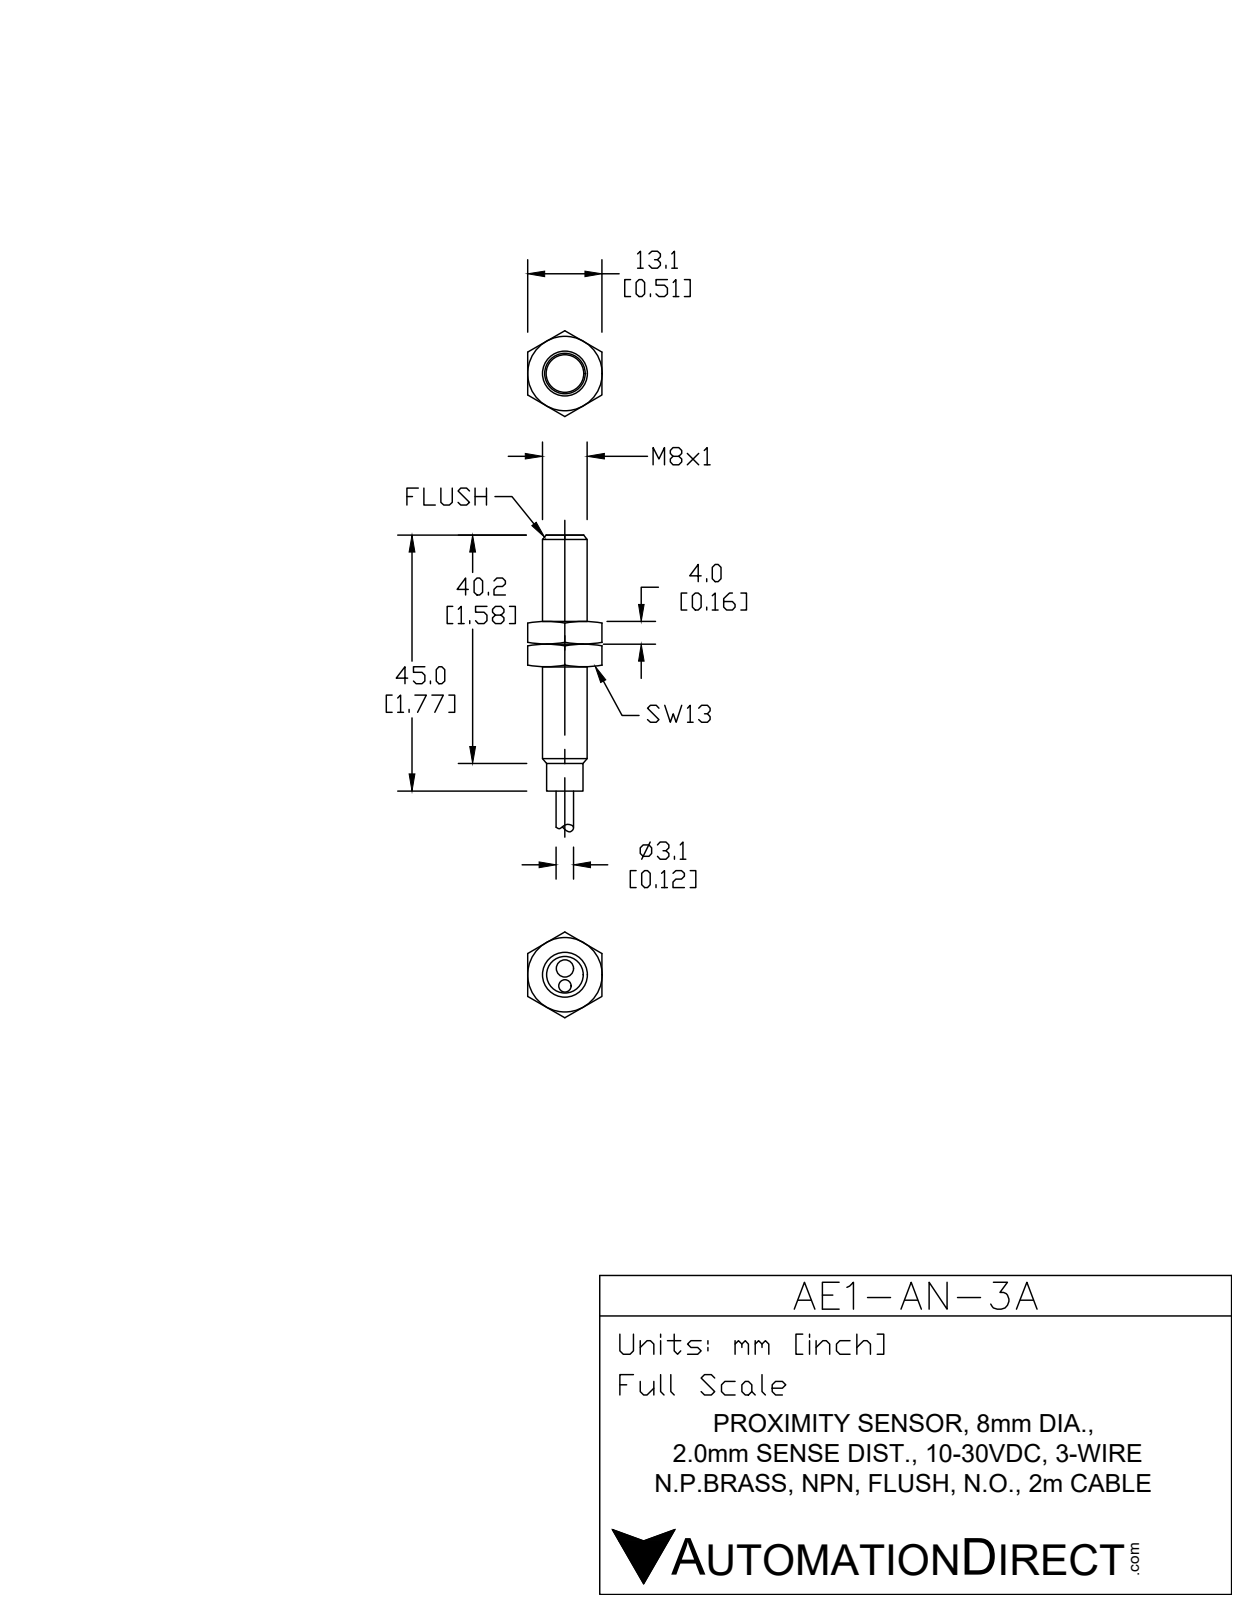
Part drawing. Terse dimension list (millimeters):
name: AE1-AN-3A
written by: SolidWorks 2017 (AUTOMOTIVE_DESIGN)
unit: mm
bodies: 4 solids, 30 faces (10 planar, 12 cylindrical, 8 other)
size: 82.6 × 8 × 8
volume: 2 430 mm³; area: 1 745 mm²
holes: 1× ⌀3.1, 1× ⌀5.8
bosses: 1× ⌀8, 1× ⌀6.5, 1× ⌀6.5
face distances: 39.9, 40.2, 44.5, 44.2, 4.3, 2.4, 42.6, 42.3, 1.9, 82.6
hole spacings: 1.1
